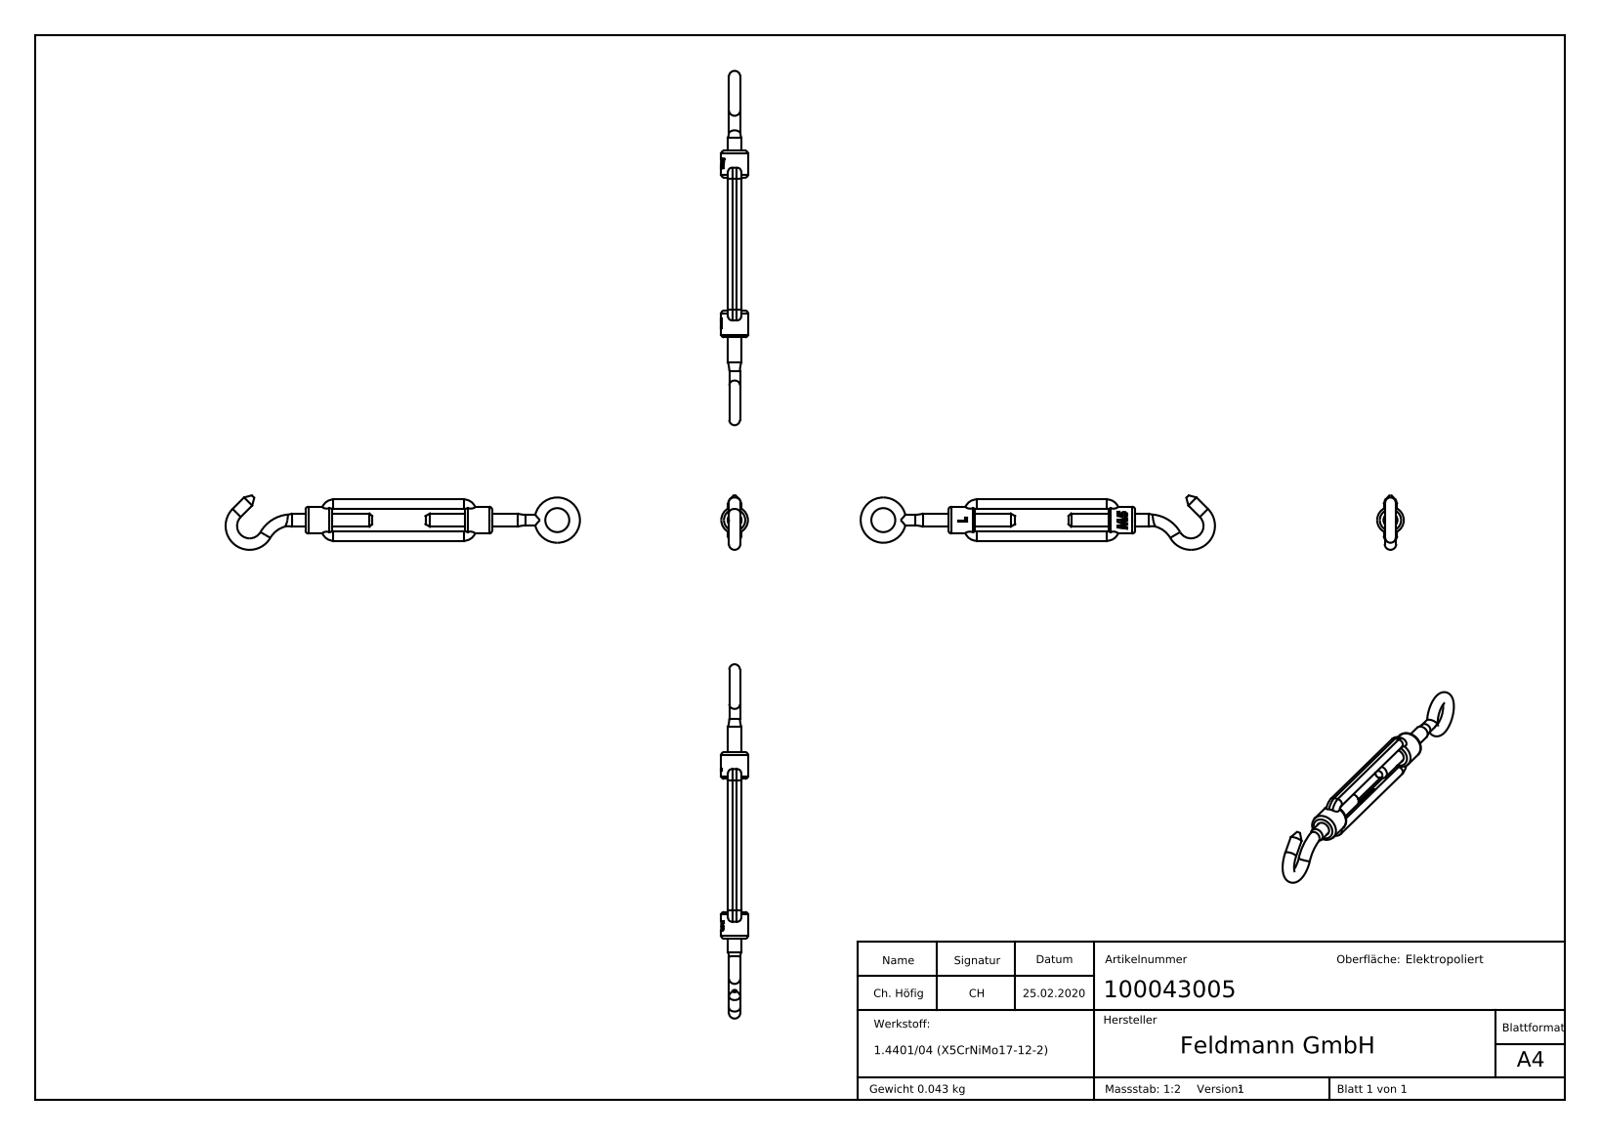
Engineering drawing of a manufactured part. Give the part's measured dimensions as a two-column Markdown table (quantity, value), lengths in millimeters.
| quantity | value |
| --- | --- |
| part name | 10004300X Teil1_100043005 Teil1; 10004300X Teil3_100043005 Teil3; 10004300X Teil2_100043005 Teil2; 100043005 |
| STEP written by | SolidWorks 2015 (CONFIG_CONTROL_DESIGN) |
| units | millimeters |
| bodies | 3 solids, 343 faces (134 planar, 31 cylindrical, 178 other) |
| overall size | 133 × 20.44 × 10 |
| volume | 5 355 mm³ |
| surface area | 4 768 mm² |
| round holes (diameter × count) | 4.2 × 1 |
| round bosses / shafts (diameter × count) | 10 × 1, 5 × 1, 4.3 × 1, 4 × 1 |
| partial cylindrical surfaces (radius × count) | 1 × 4, 1.75 × 4, 4.5 × 4, 4.98 × 1 |
| main face-to-face distances | 3.5, 12, 15.5, 8.5, 10, 60, 50, 70, 25, 45 |
